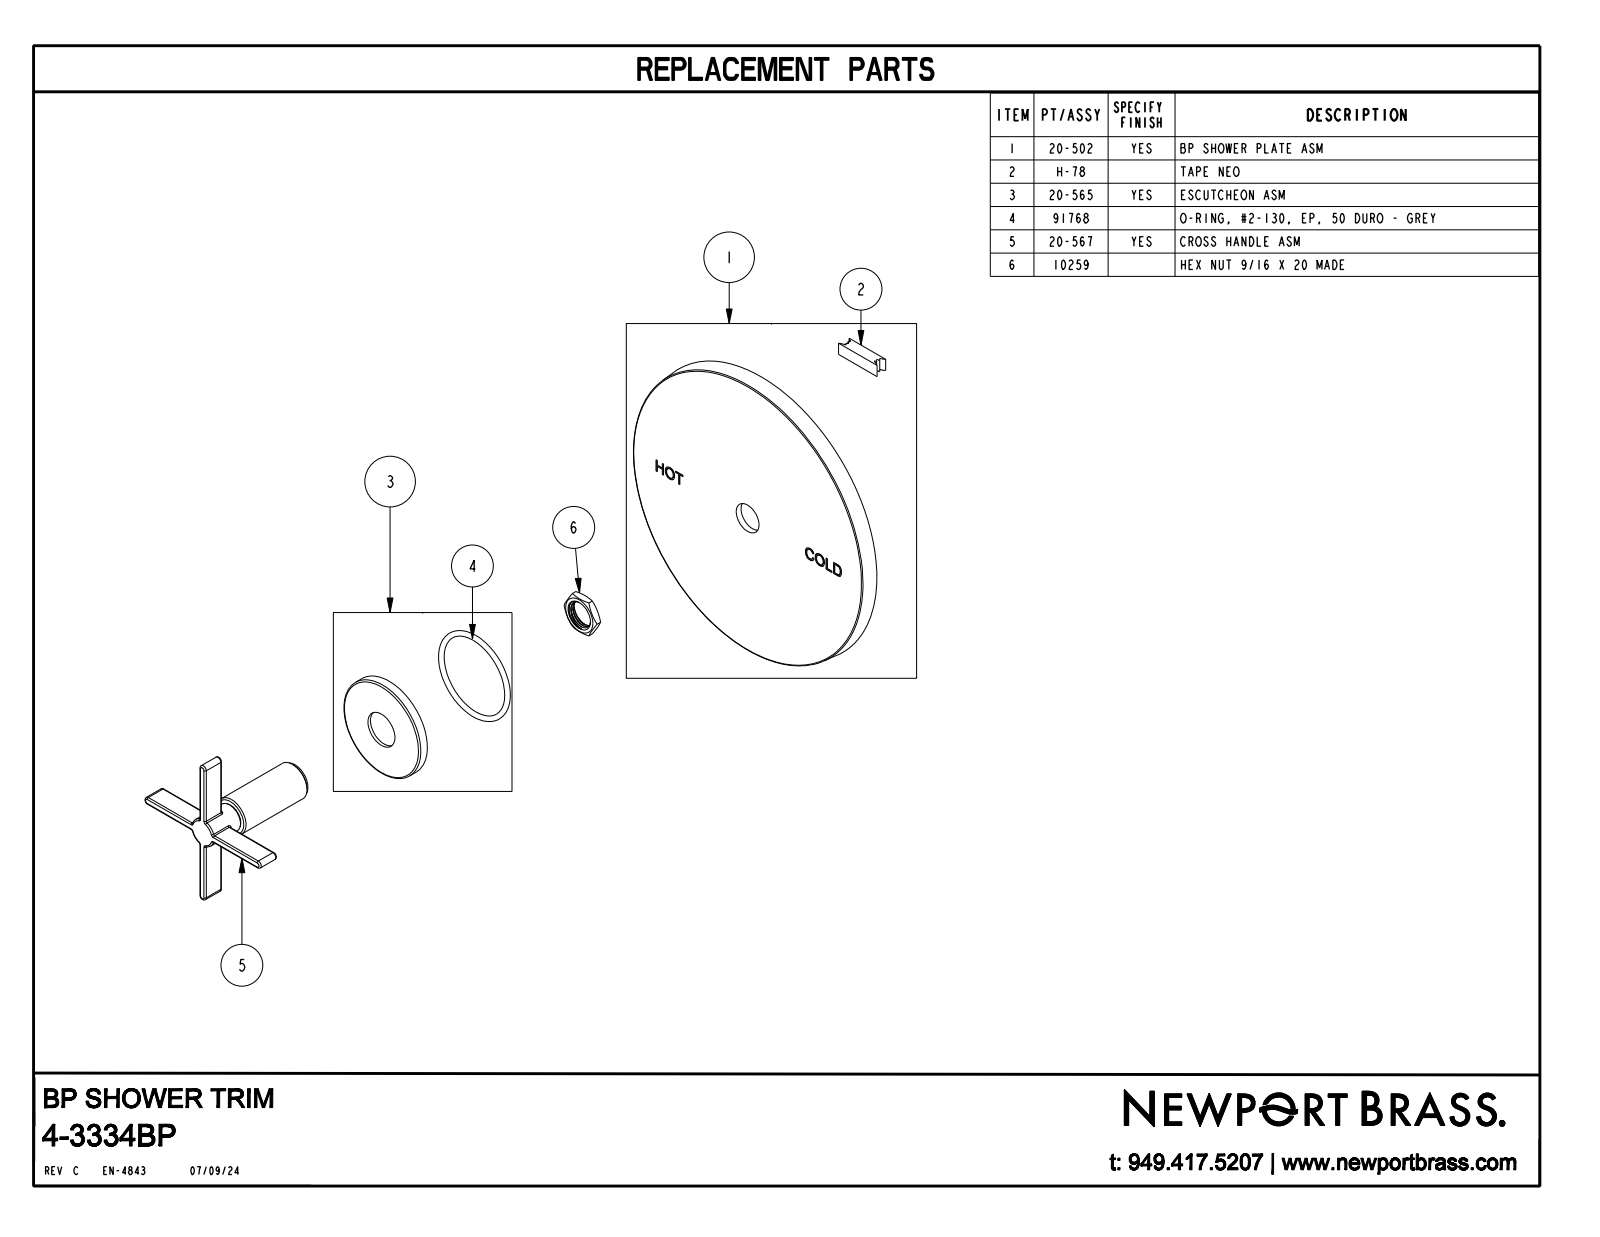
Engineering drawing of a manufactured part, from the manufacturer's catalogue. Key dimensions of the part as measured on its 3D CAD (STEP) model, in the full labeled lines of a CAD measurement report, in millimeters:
Part name (STEP PRODUCT): 30749; 20-502_ASM; 13532; 20-565_ASM (+5 more)
STEP written by: CREO PARAMETRIC BY PTC INC, 2018400 (CONFIG_CONTROL_DESIGN)
Units: millimetres
Bodies: 4 solids, 377 faces (120 planar, 110 cylindrical, 147 other)
Overall size (bounding box): 152.4 × 152.2 × 71.9
Volume: 82 410 mm³ · Surface area: 57 830 mm²
Round holes (diameter × count): ⌀2.8 ×1, ⌀9.1 ×1, ⌀10.1 ×1, ⌀10.2 ×1, ⌀13.1 ×1, ⌀13.6 ×1, ⌀15 ×1, ⌀15.2 ×1, ⌀17.8 ×1, ⌀40.6 ×1, ⌀48 ×1
Round bosses / shafts (diameter × count): ⌀50.8 ×1, ⌀41.9 ×1, ⌀19.1 ×1, ⌀18.5 ×1, ⌀17.3 ×1, ⌀14.3 ×1, ⌀13 ×1
Partial cylindrical surfaces — rounded edges, fillets, slot ends (radius × count): R0.8 ×16, R1.9 ×4, R3.5 ×1
Main face-to-face distances: 3.2, 8.3, 5.1, 5.7, 8.9, 14, 1.3, 3.8, 12.7, 7
